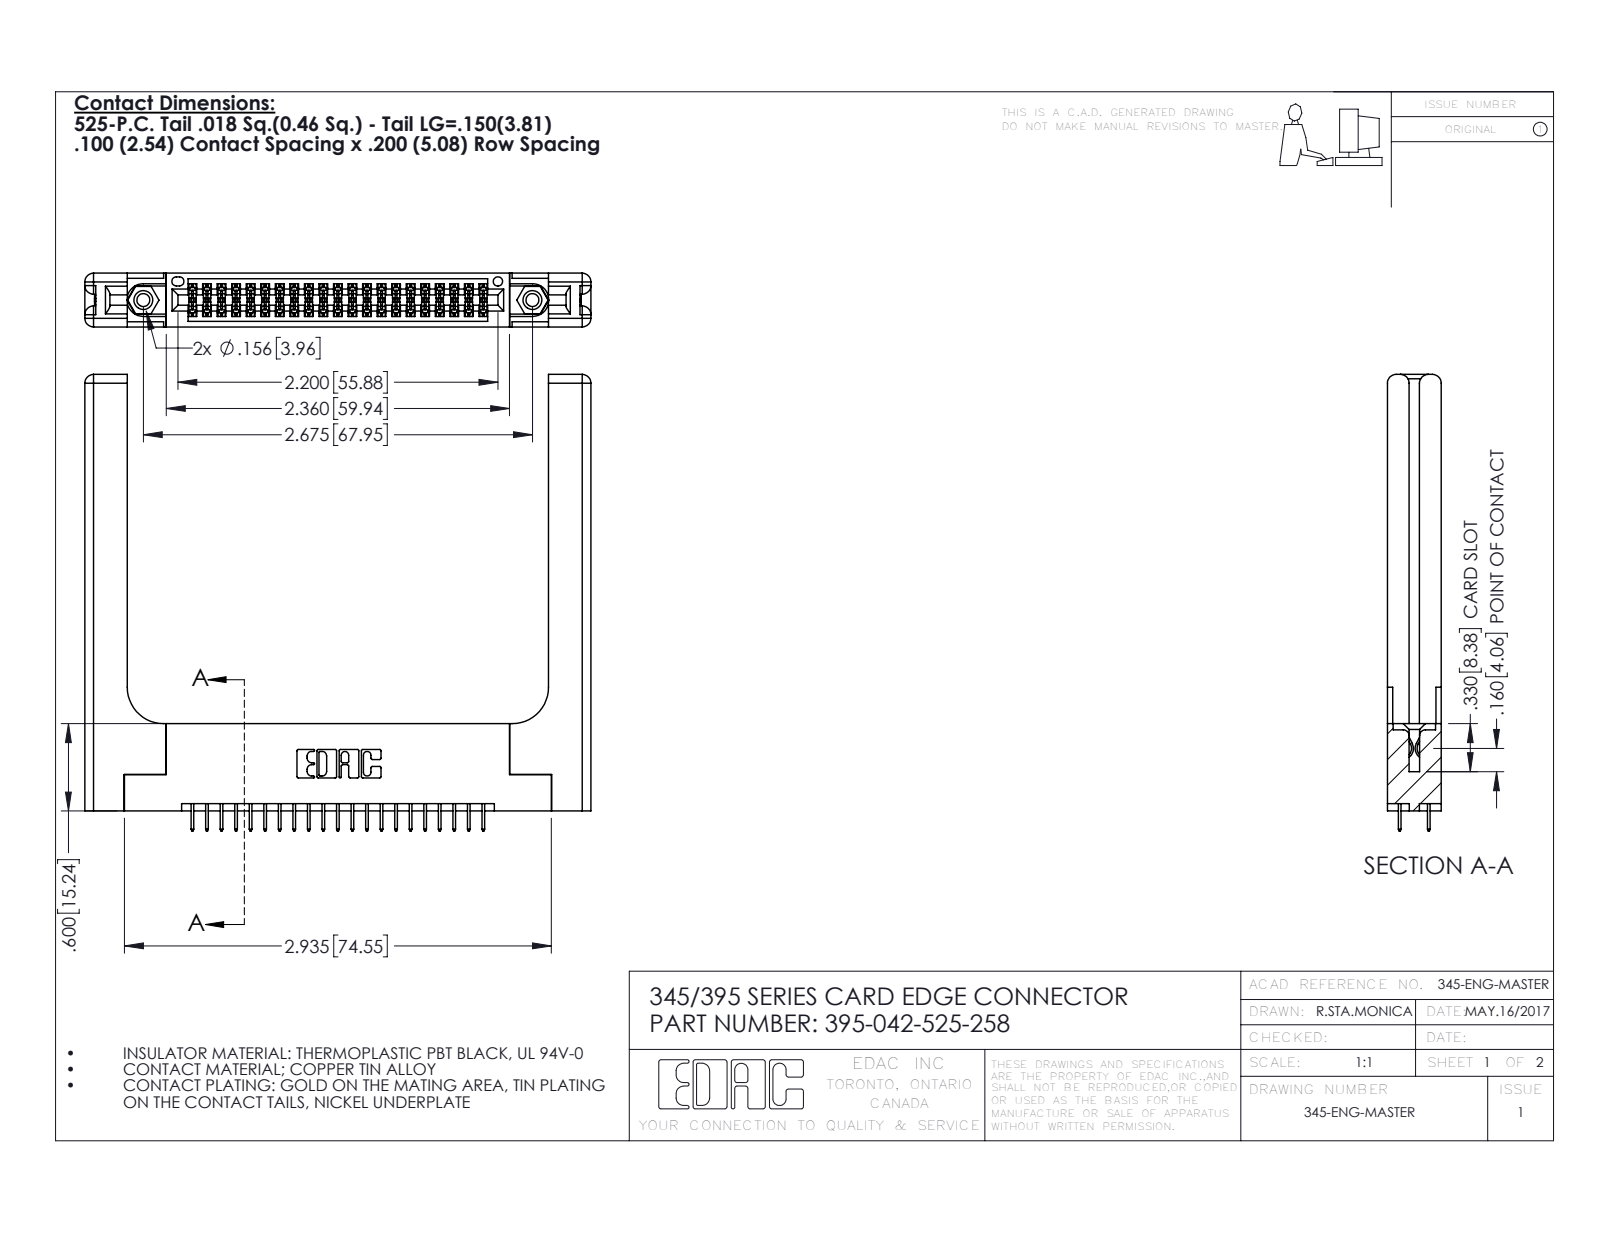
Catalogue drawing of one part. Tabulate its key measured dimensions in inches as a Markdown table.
| quantity | value |
| --- | --- |
| part name | 345 Part_Flush Mounting Lugs - 0.156 Dia-TH; 345-250-001_345-250-001-102; 345-220-058_345-220-058; 395-042-525-258 (+1 more) |
| STEP written by | SolidWorks 2020 (CONFIG_CONTROL_DESIGN) |
| units | inches |
| bodies | 47 solids, 2650 faces (1866 planar, 724 cylindrical, 60 other) |
| overall size | 3.479 × 3.137 × 0.37 |
| volume | 1.025 in³ |
| surface area | 25.95 in² |
| round holes (diameter × count) | 0.089 × 2, 0.125 × 2, 0.156 × 2, 0.064 × 1 |
| round bosses / shafts (diameter × count) | 0.155 × 2 |
| partial cylindrical surfaces (radius × count) | 0.006 × 84, 0.01 × 22, 0.06 × 16, 0.007 × 6, 0.031 × 6, 0.026 × 3, 0.014 × 2, 0.019 × 2 |
| main face-to-face distances | 0.37, 0.072, 0.298, 0.2, 0.15, 0.148, 0.077, 0.22, 0.098, 0.272 |
| hole center spacings | 0.27, 2.441, 2.675 |
